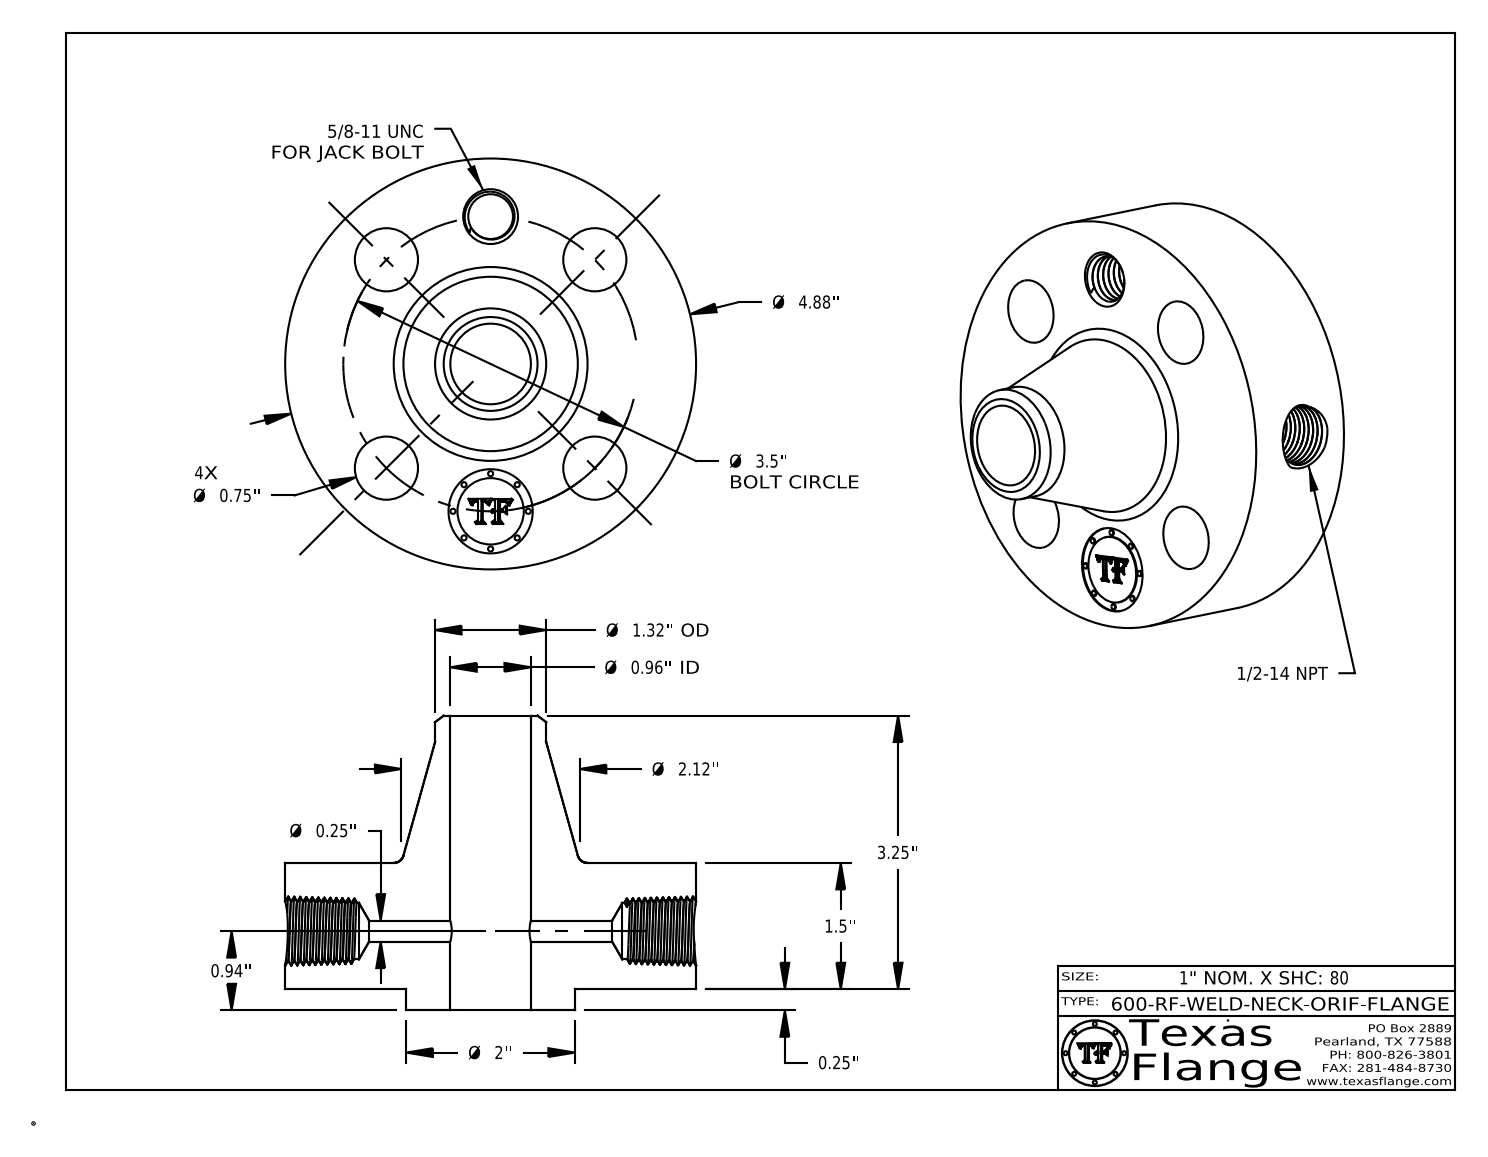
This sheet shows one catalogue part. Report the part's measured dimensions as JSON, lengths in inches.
{"part_name": "600-RF-WELD-NECK", "step_written_by": "CATIA V5 STEP AP214 (AUTOMOTIVE_DESIGN)", "units": "inches", "bodies": {"solids": 1, "faces": 764, "planar": 369, "cylindrical": 87, "other": 308}, "overall_size": [4.88, 4.88, 3.5], "volume_in3": 26.22, "surface_area_in2": 100.3, "round_holes": [[0.75, 4], [0.25, 1], [0.531, 1], [0.672, 1], [0.957, 1], [1, 1]], "round_bosses_or_shafts": [[0.061, 8], [4.88, 1], [2, 1], [1.32, 1], [0.788, 1]], "face_to_face_distances": [1.5, 1.75, 0.25, 1.735, 1.485, 0.015, 3.5, 3.25, 1.765, 0.298], "hole_center_spacings": [1.75, 1.339, 2.475, 3.233, 3.5]}
